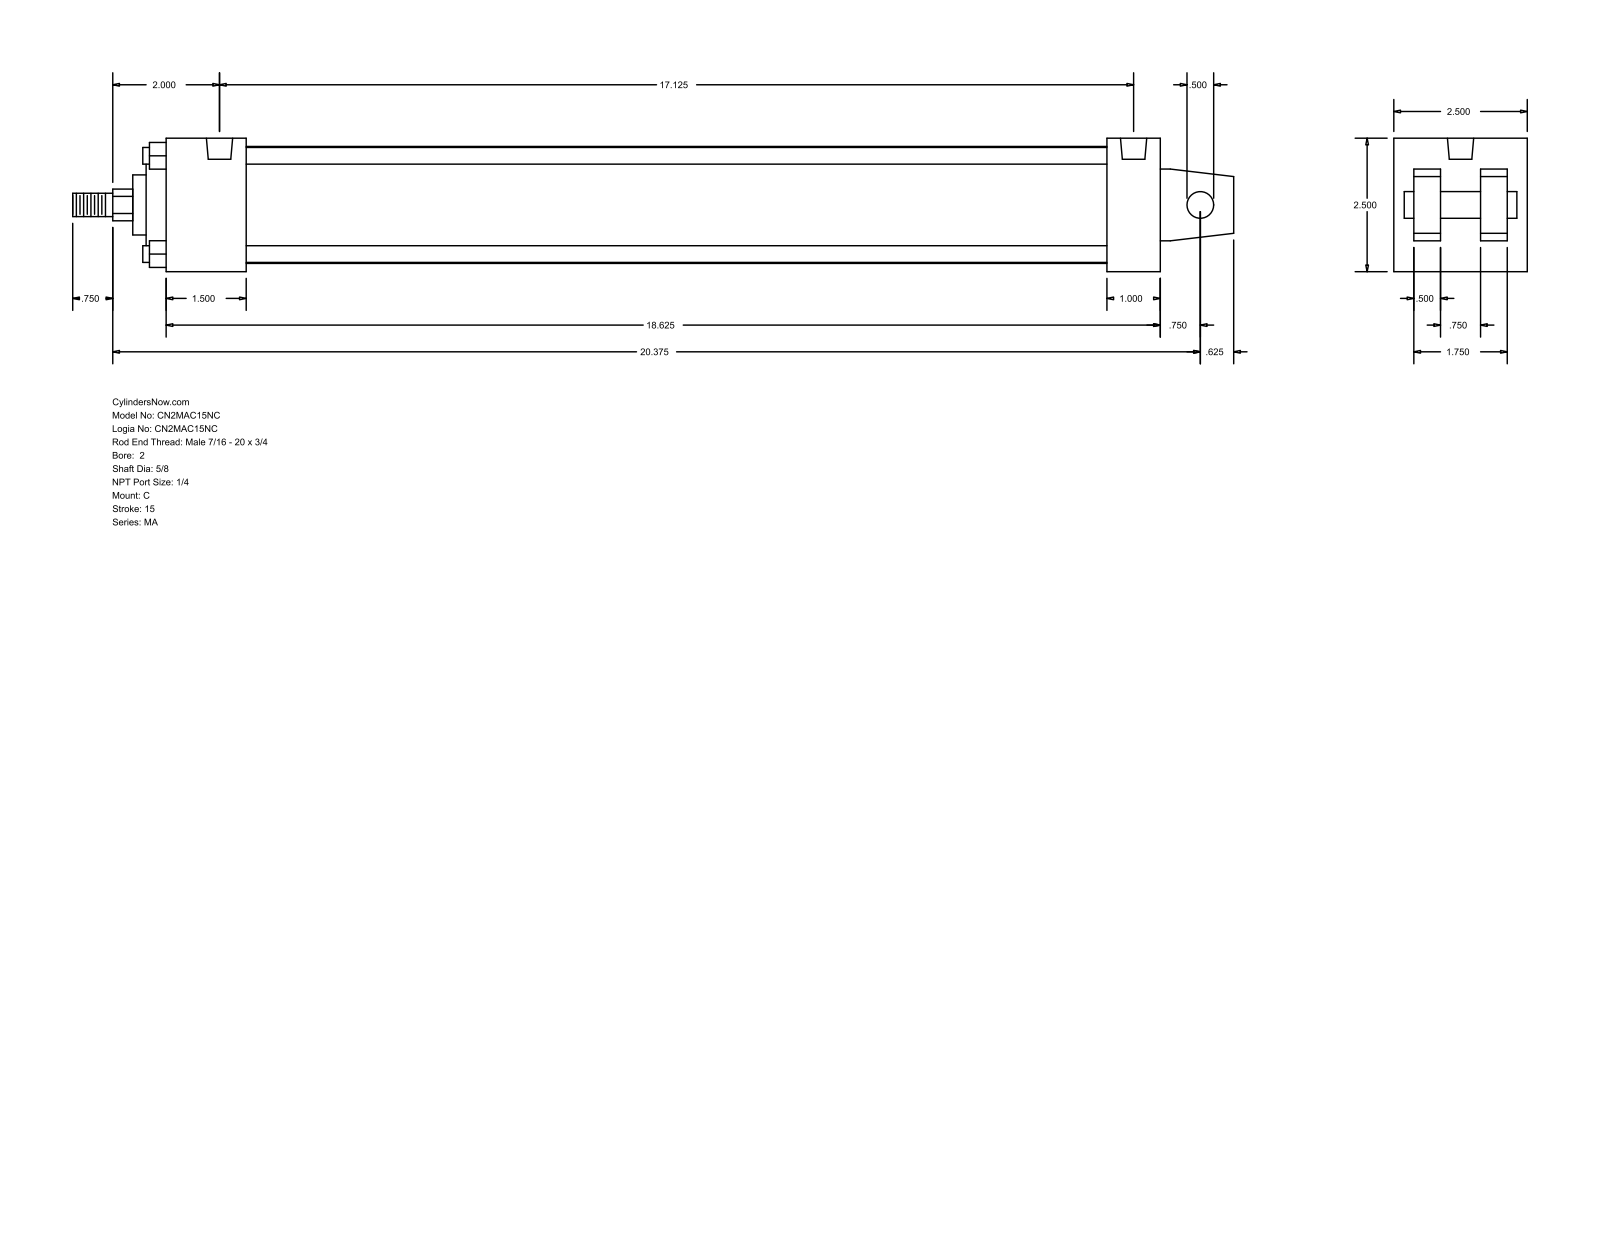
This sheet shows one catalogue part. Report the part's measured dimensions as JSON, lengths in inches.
{"part_name": "MA_C__0200_0.625", "step_written_by": "GSSL Pune (CONFIG_CONTROL_DESIGN)", "units": "inches", "bodies": {"solids": 0, "faces": 105, "planar": 77, "cylindrical": 28, "other": 0}, "overall_size": [21.75, 2.5, 2.5], "round_holes": [[0.313, 4], [0.492, 2]], "round_bosses_or_shafts": [[0.313, 4], [2.19, 1], [2, 1], [1.125, 1], [0.625, 1], [0.5, 1], [0.437, 1]], "partial_cylinders_radius": [[0.297, 1]], "face_to_face_distances": [2.5, 0.375, 0.5, 0.875, 1.625, 2.125, 1.25, 1.5, 18.625, 17.125], "hole_center_spacings": [17.125]}
